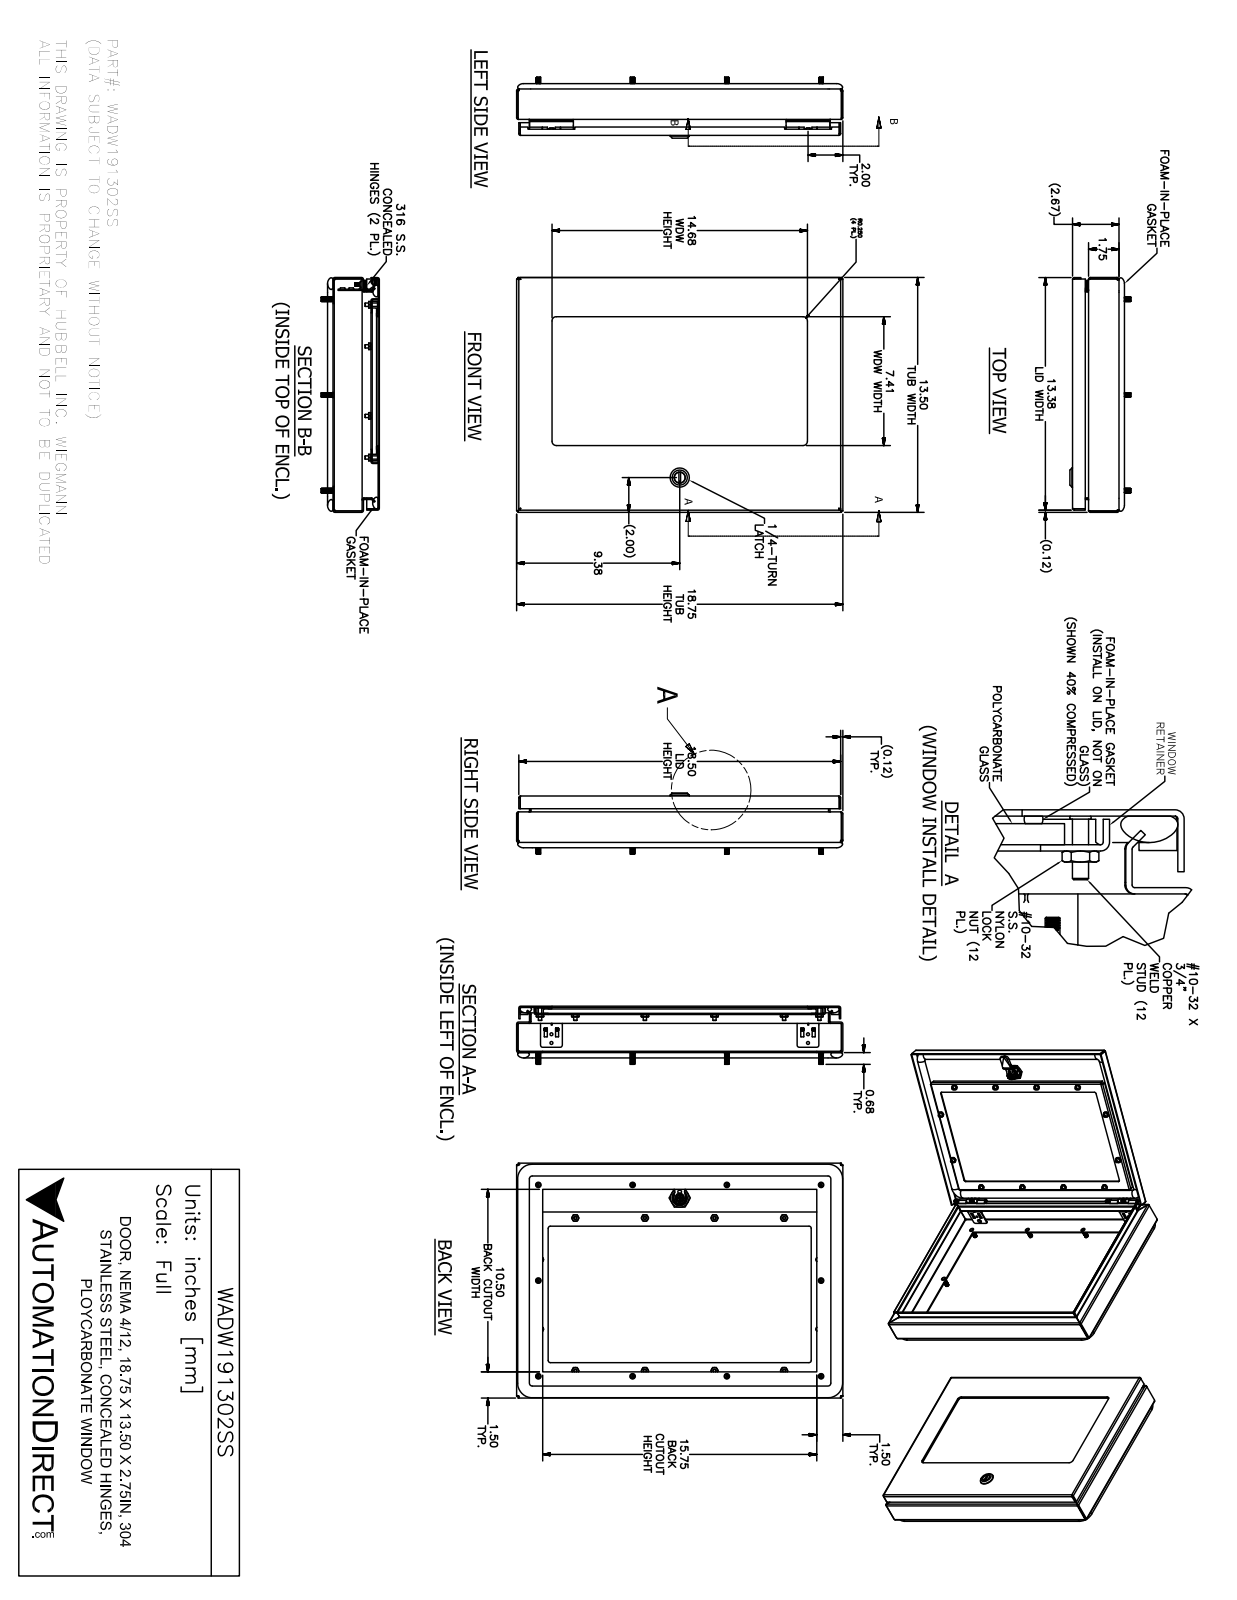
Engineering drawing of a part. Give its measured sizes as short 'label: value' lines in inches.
name: WADW191302SS
written by: SolidWorks 2017 (AUTOMOTIVE_DESIGN)
unit: in
bodies: 65 solids, 1951 faces (724 planar, 625 cylindrical, 602 other)
size: 18.75 × 13.5 × 3.5
volume: 94.24 in³; area: 1 551 in²
holes: 14× ⌀0.156, 12× ⌀0.281, 9× ⌀0.249, 4× ⌀0.093, 4× ⌀0.152, 4× ⌀0.167, 4× ⌀0.172, 4× ⌀0.188, 1× ⌀0.187, 1× ⌀0.197, 1× ⌀0.315, 1× ⌀0.394
bosses: 20× ⌀0.25, 12× ⌀0.19, 4× ⌀0.36, 4× ⌀0.32, 4× ⌀0.256, 4× ⌀0.164, 4× ⌀0.131, 1× ⌀1.102
rounds: 34× R0.031, 30× R0.012, 26× R0.05, 24× R0.105, 20× R0.125, 18× R0.016, 13× R0.02, 8× R0.032
face distances: 0.074, 0.411, 0.337, 0.25, 0.087, 0.161, 2.593, 2.182, 1.676, 2.432
hole spacings: 4, 9.653, 14.746, 5.5, 6.706, 8, 8.785, 11.857
